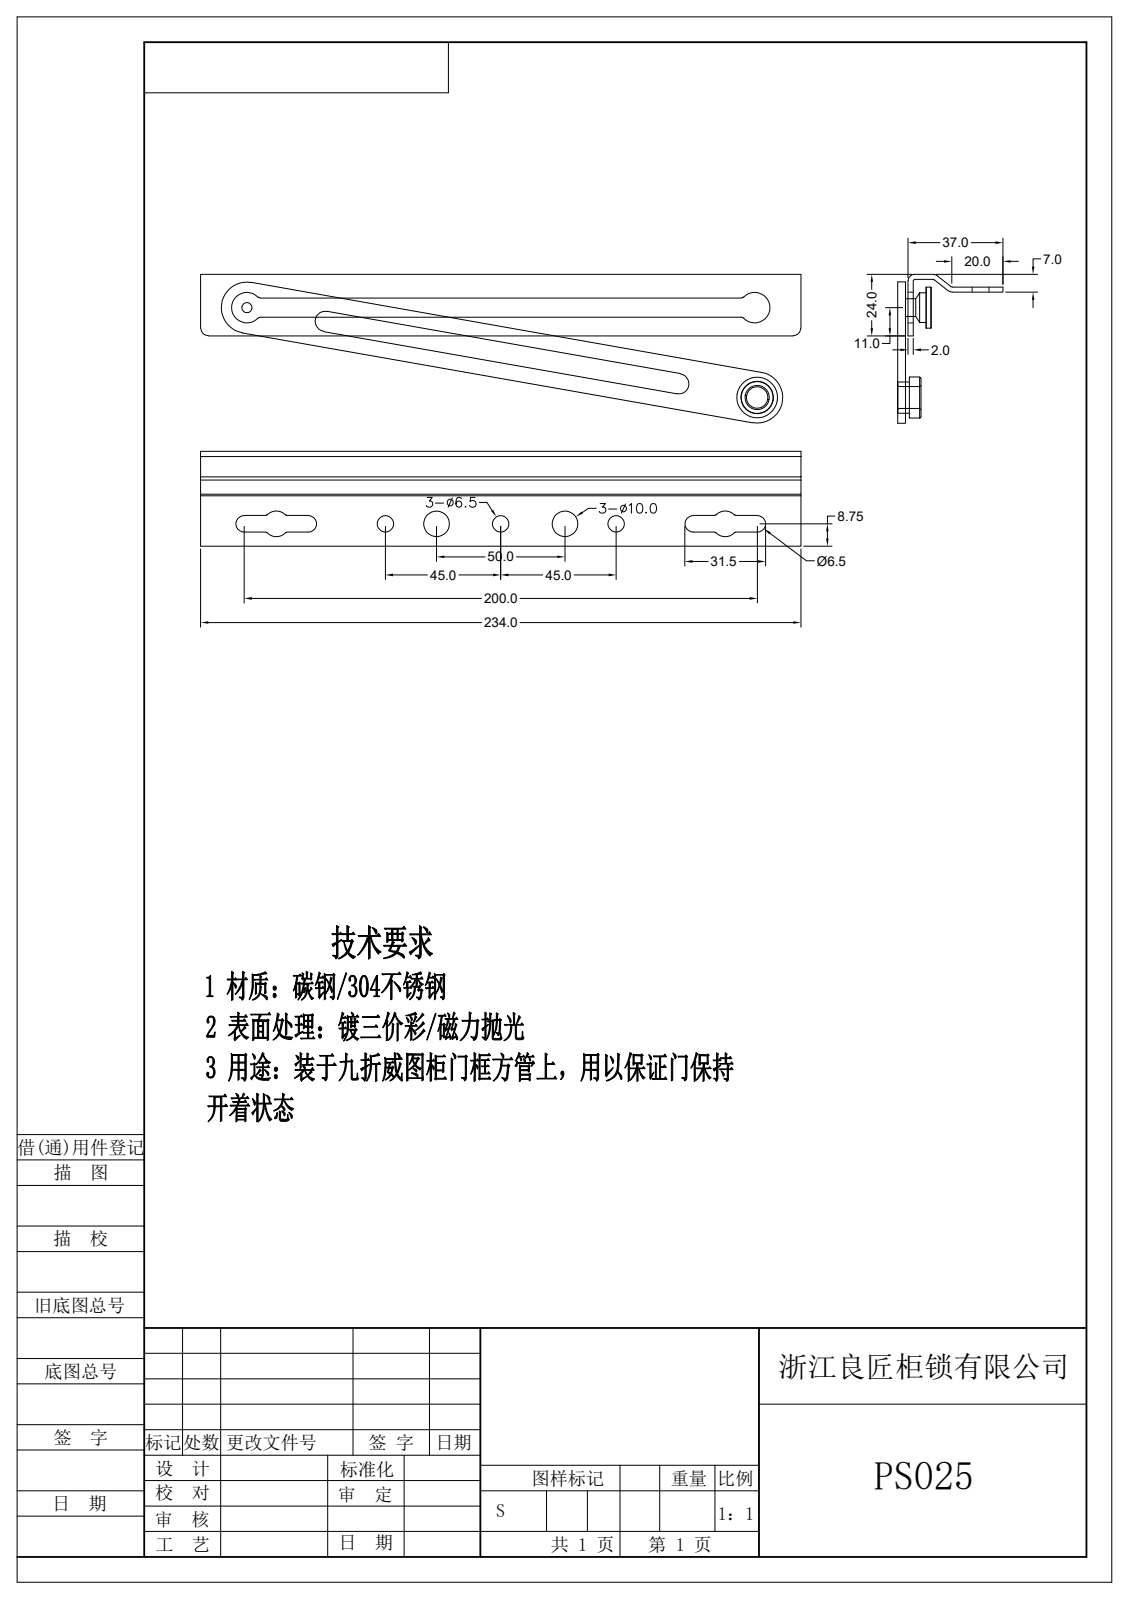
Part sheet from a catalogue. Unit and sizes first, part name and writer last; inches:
Units: inches
Overall size (bounding box): 9.213 × 2.287 × 1.772
Round holes (diameter × count): ⌀0.256 ×3, ⌀0.394 ×2
Round bosses / shafts (diameter × count): ⌀0.63 ×2, ⌀0.453 ×1, ⌀0.335 ×1, ⌀0.276 ×1
Partial cylindrical surfaces — rounded edges, fillets, slot ends (radius × count): R0.02 ×15, R0.039 ×4, R0.128 ×4, R0.098 ×3, R0.157 ×2, R0.197 ×2, R0.236 ×2, R0.394 ×2
Main face-to-face distances: 0.079, 0.118, 0.197, 0.157, 0.236, 0.039, 0.276, 0.177, 0.285, 0.581
Hole centre spacings: 1.772, 0.787, 0.984, 2.559, 2.756, 3.543
Volume: 2.378 in³ · Surface area: 61.16 in²
Bodies: 5 solids, 117 faces (37 planar, 56 cylindrical, 24 other)
STEP written by: Rhino 8.5 (CONFIG_CONTROL_DESIGN)
